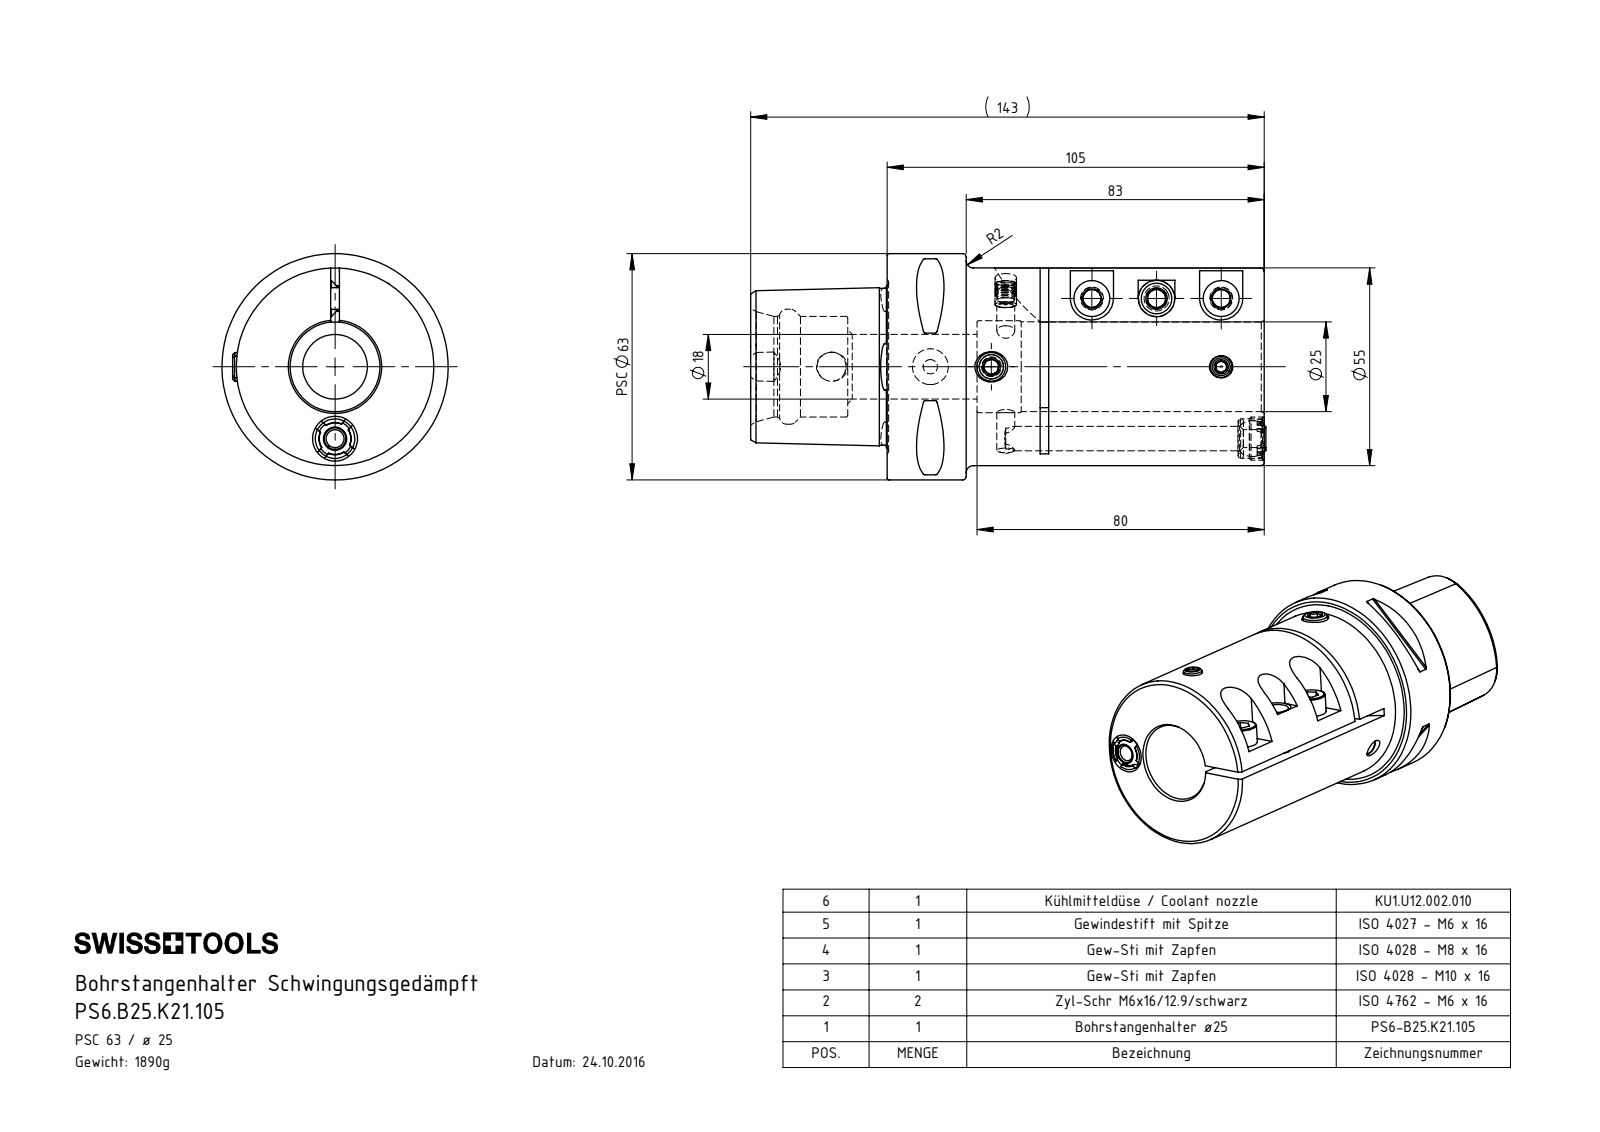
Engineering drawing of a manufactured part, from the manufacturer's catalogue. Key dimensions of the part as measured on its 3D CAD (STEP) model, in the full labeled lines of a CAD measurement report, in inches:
Part name (STEP PRODUCT): PS6.B25.K21.105; DIN 3771 - 8x1.5; KU1-U12.002.010_A; ISO 4028 - M8 x 16 (+7 more)
STEP written by: SolidWorks 2017 (AUTOMOTIVE_DESIGN)
Units: inches
Bodies: 11 solids, 302 faces (129 planar, 61 cylindrical, 112 other)
Overall size (bounding box): 5.649 × 2.48 × 2.48
Volume: 14.72 in³ · Surface area: 79.62 in²
Round holes (diameter × count): ⌀0.197 ×5, ⌀0.157 ×2, ⌀0.252 ×2, ⌀0.268 ×2, ⌀0.319 ×1, ⌀0.335 ×1, ⌀0.394 ×1, ⌀0.433 ×1, ⌀0.709 ×1, ⌀0.984 ×1, ⌀1.008 ×1, ⌀1.102 ×1
Round bosses / shafts (diameter × count): ⌀0.236 ×4, ⌀0.394 ×3, ⌀2.48 ×1, ⌀2.165 ×1, ⌀0.472 ×1, ⌀0.315 ×1, ⌀0.276 ×1, ⌀0.217 ×1
Partial cylindrical surfaces — rounded edges, fillets, slot ends (radius × count): R0.02 ×8, R0.236 ×3, R0.173 ×1, R0.201 ×1, R2.047 ×1, R2.165 ×1
Main face-to-face distances: 0.094, 4.134, 2.362, 1.677, 2.457, 1.772, 3.268, 1.496, 3.173, 5.63
Hole centre spacings: 0.709, 0.669, 0.748, 0.787, 1.03, 1.083, 1.332, 1.417
